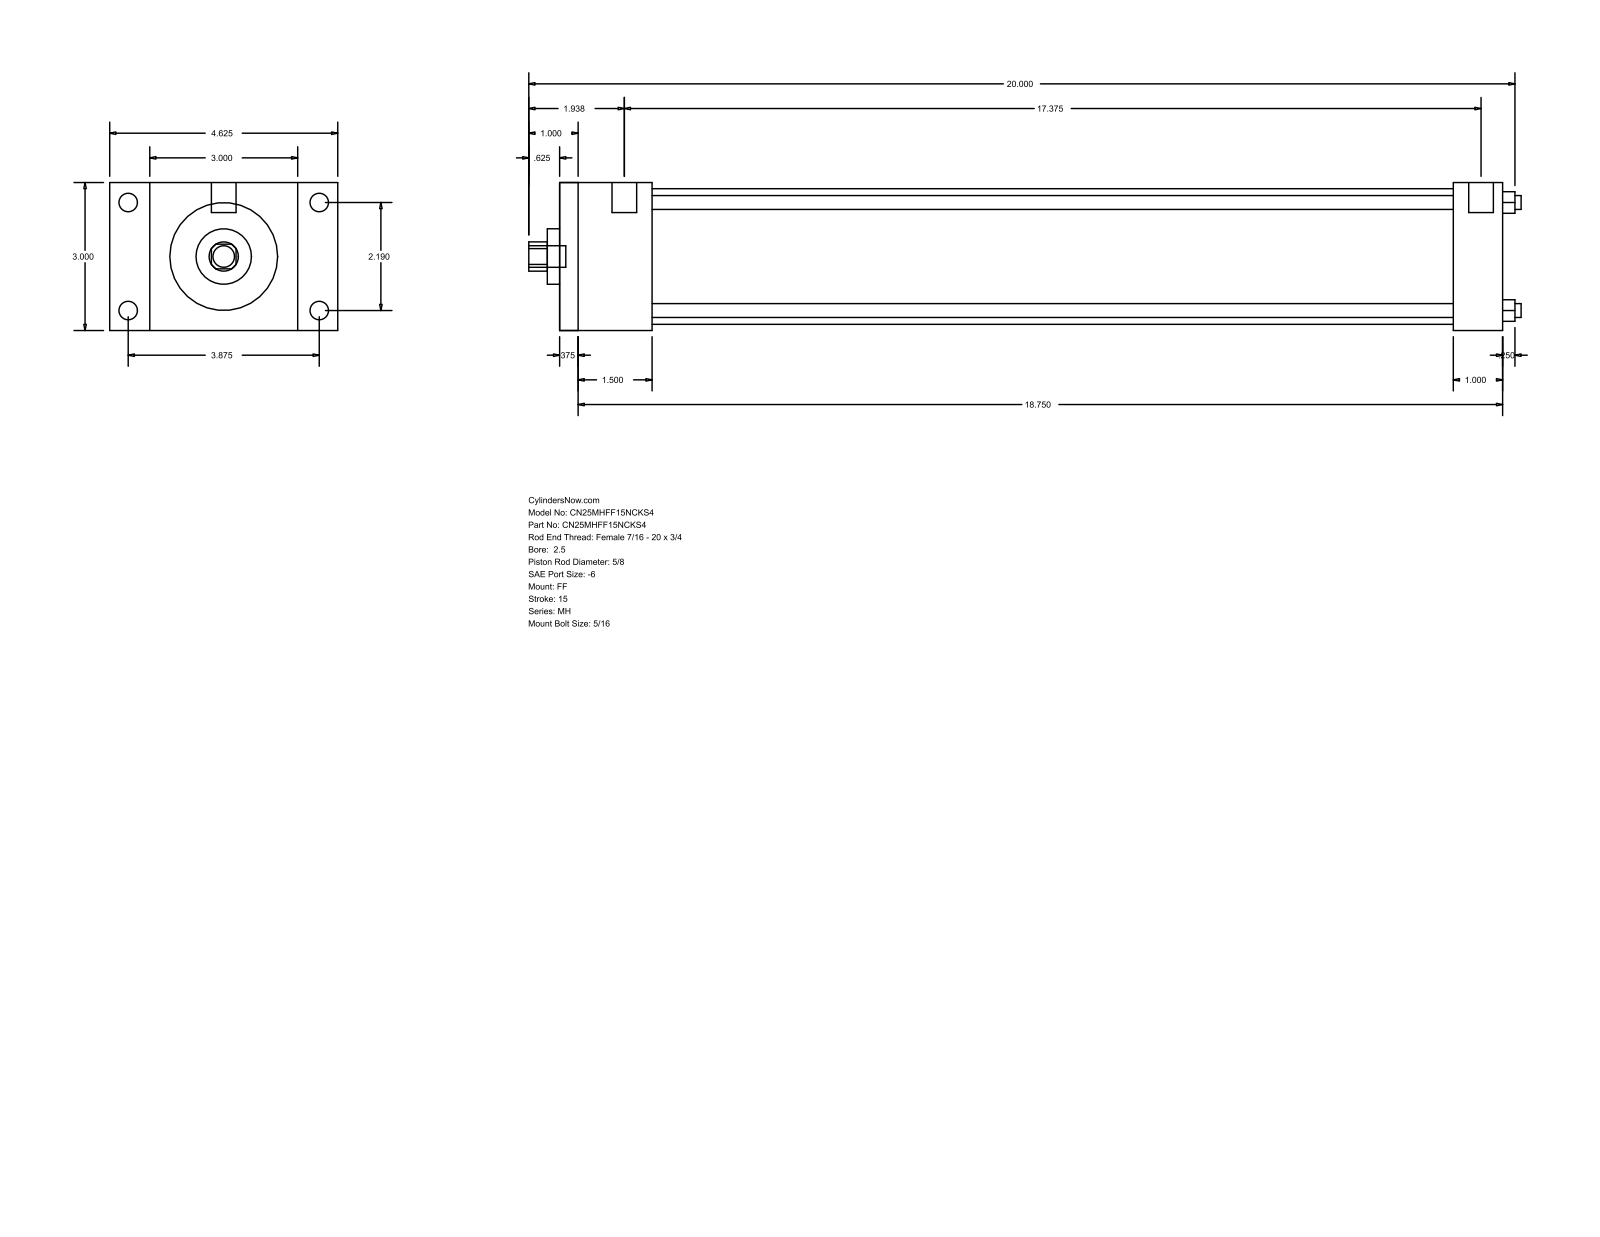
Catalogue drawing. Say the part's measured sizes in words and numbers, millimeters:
The part is named "MH_FF__0250_0.625". Its 3-D file was written by "GSSL Pune (CONFIG_CONTROL_DESIGN)". It is 0 solids with 92 faces: 64 planar, 28 cylindrical and 0 other. Overall it measures 511.18 by 117.47 by 76.2 millimeters. Round holes: 4 of diameter 7.14, 1 of diameter 15.88, 1 of diameter 28.57, 1 of diameter 69.85. Round bosses or shafts: 4 of diameter 9.53, 4 of diameter 5.56, 2 of diameter 12.7, 1 of diameter 11.11. Partial cylindrical surfaces (rounded edges, fillets, slot ends): 1 of radius 7.54. The main face-to-face distances are 76.2, 485.77, 9.52, 476.25, 25.4, 47.62, 460.37, 38.1, 450.85, 412.75. The hole center spacings are 39.33, 55.62, 78.66.
